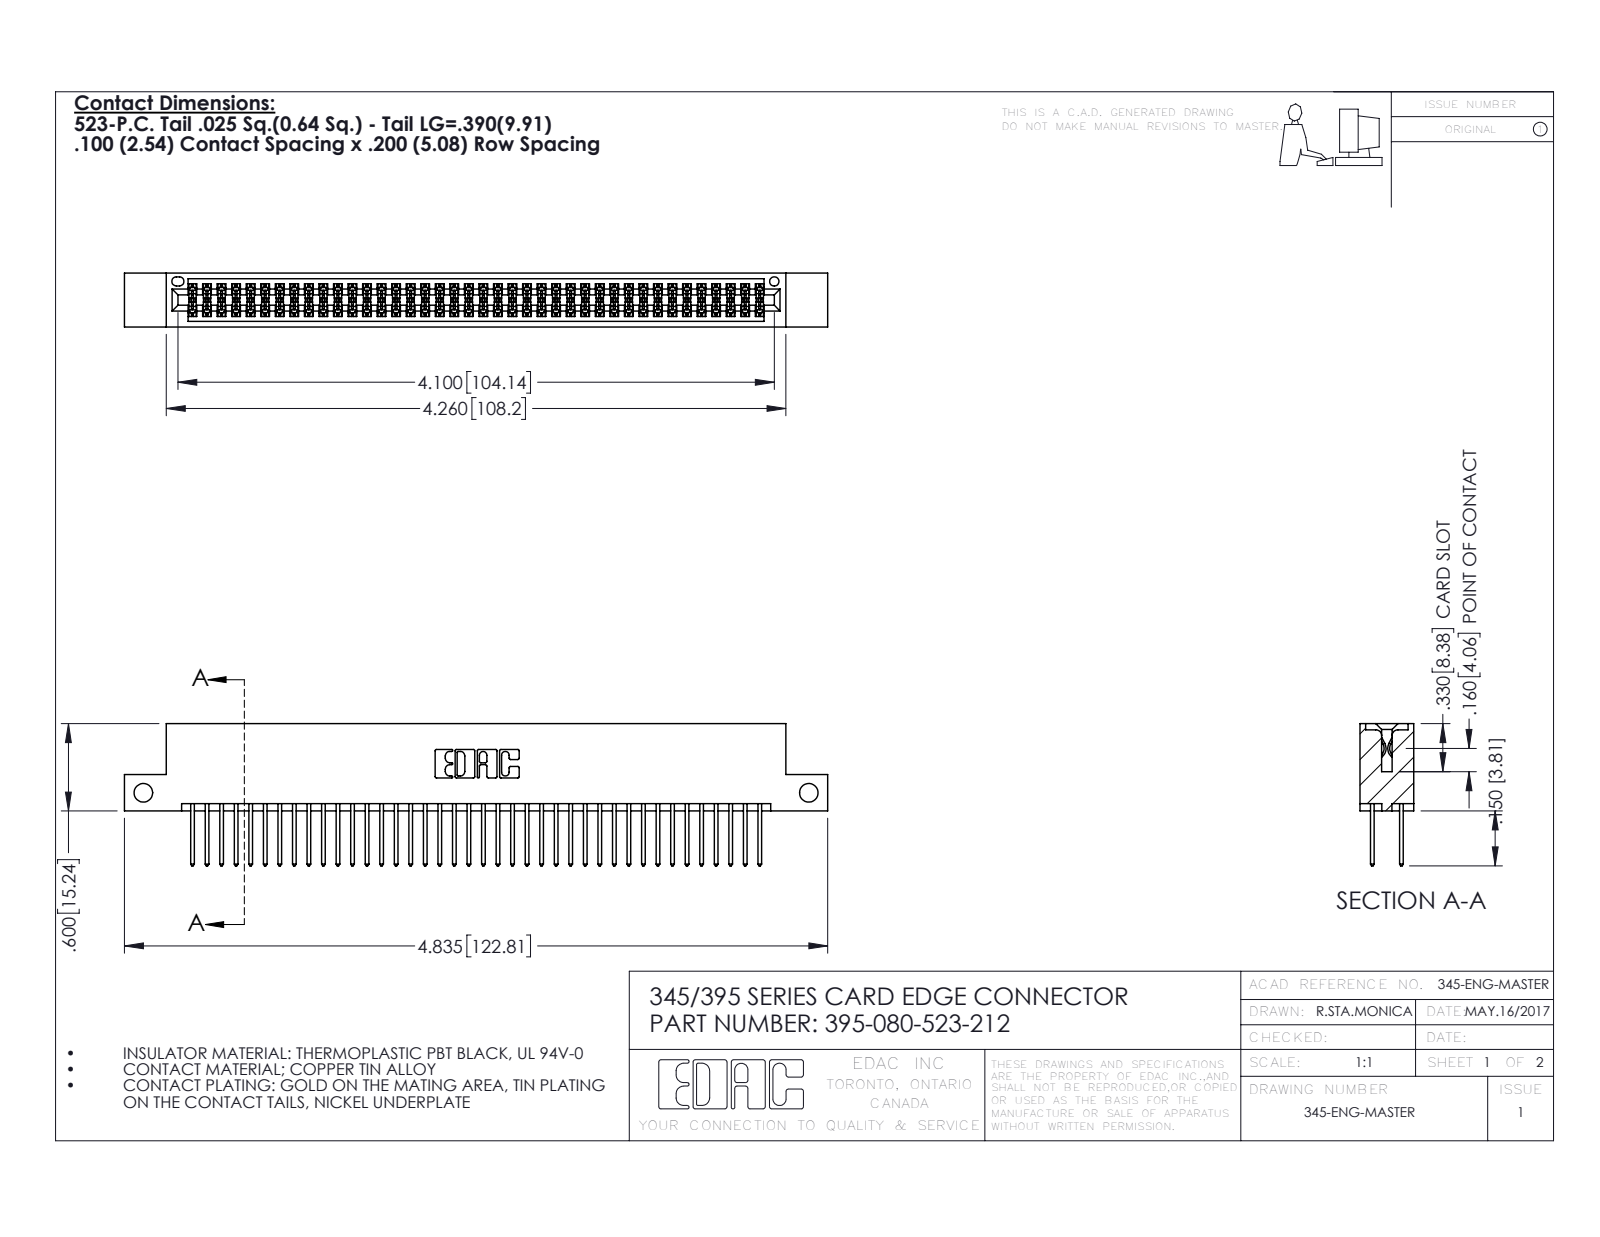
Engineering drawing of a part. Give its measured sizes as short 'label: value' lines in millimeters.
name: 345-292-001_345-293-123; 395-080-523-212; 345 Part_Flush Mounting Lugs - Side Mount
written by: SolidWorks 2016 (CONFIG_CONTROL_DESIGN)
unit: mm
bodies: 81 solids, 4126 faces (2720 planar, 1406 cylindrical, 0 other)
size: 122.8 × 24.8 × 9.4
volume: 12 000 mm³; area: 18 280 mm²
holes: 2× ⌀3.3, 1× ⌀1.6
rounds: 120× R0.2, 80× R0.3, 22× R0.3, 6× R0.2, 6× R0.8, 3× R0.7, 2× R0.4, 2× R0.5
face distances: 7.6, 1.8, 5.1, 2.5, 6.9, 0.6, 9.4, 5.7, 4.4, 3.8
hole spacings: 116.2
